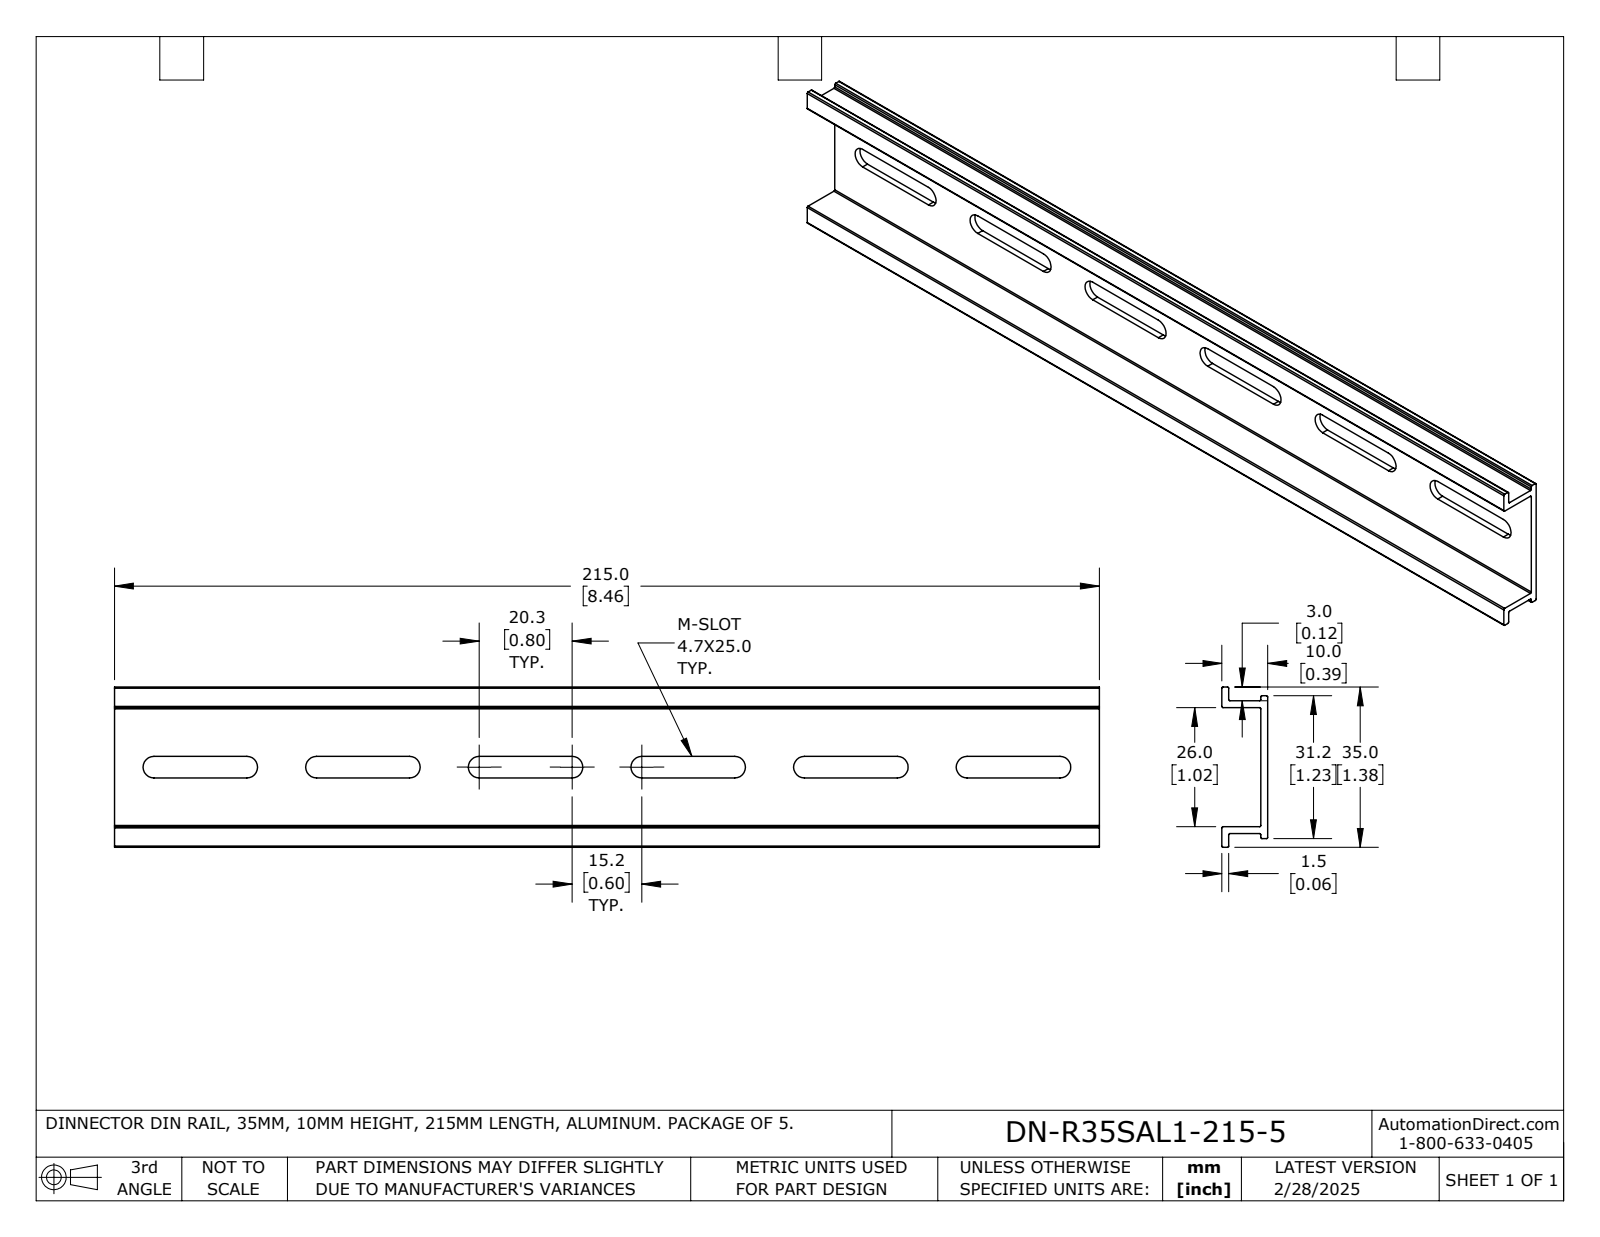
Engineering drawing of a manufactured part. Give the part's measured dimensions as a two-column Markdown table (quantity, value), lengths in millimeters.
| quantity | value |
| --- | --- |
| part name | DN-R35SAL1-215-5_Default |
| STEP written by | SolidWorks 2024 (CONFIG_CONTROL_DESIGN) |
| units | millimeters |
| bodies | 1 solid, 58 faces (30 planar, 28 cylindrical, 0 other) |
| overall size | 215 × 35 × 10 |
| volume | 16 451 mm³ |
| surface area | 22 863 mm² |
| partial cylindrical surfaces (radius × count) | 0.27 × 16, 2.35 × 12 |
| main face-to-face distances | 1.5, 27.5, 8.5, 26, 10, 29, 7, 1.1, 2.6, 28.6 |
